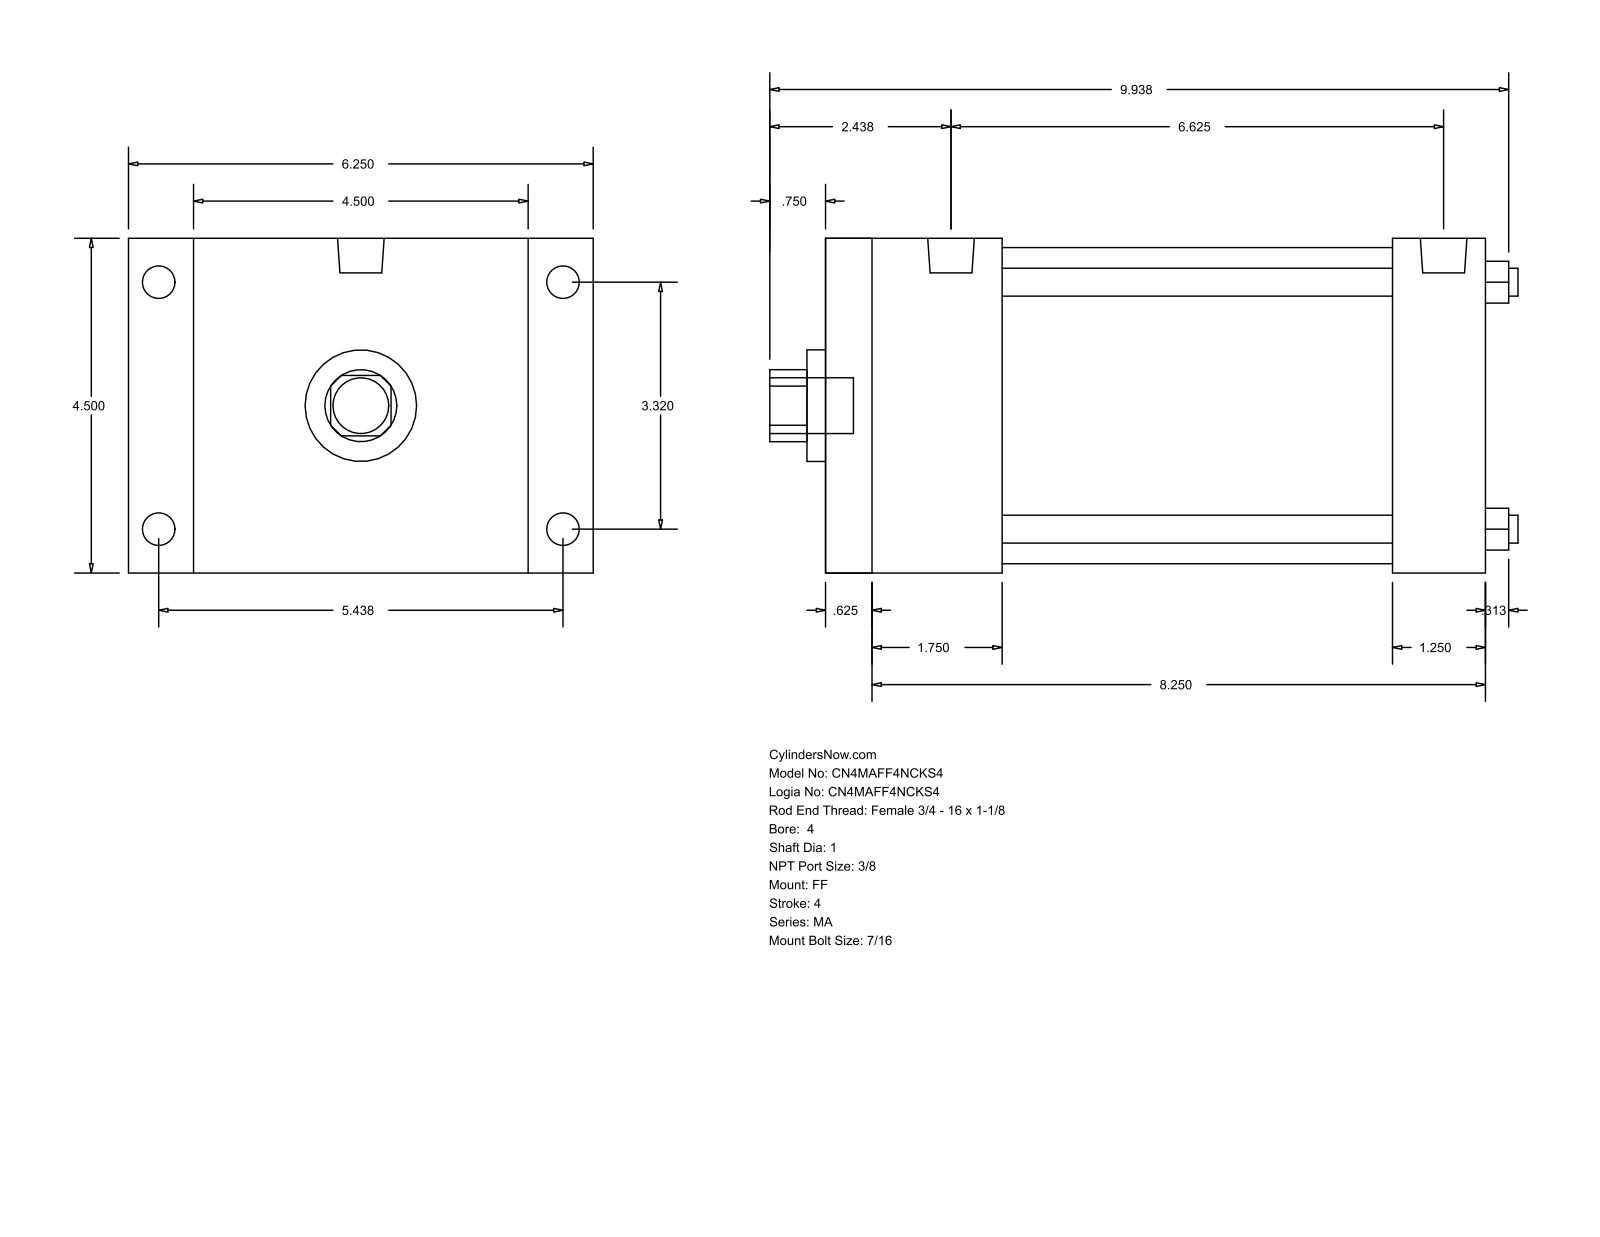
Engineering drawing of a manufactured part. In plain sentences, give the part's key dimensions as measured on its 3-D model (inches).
The part is named "MA_FF__0400_1". Its 3-D file was written by "GSSL Pune (CONFIG_CONTROL_DESIGN)". It is 0 solids with 92 faces: 64 planar, 28 cylindrical and 0 other. Overall it measures 10.063 by 6.25 by 4.5 inches. Round holes: 4 of diameter 0.375, 1 of diameter 1, 1 of diameter 1.5, 1 of diameter 4.25. Round bosses or shafts: 8 of diameter 0.437, 2 of diameter 0.627, 1 of diameter 0.75. Partial cylindrical surfaces (rounded edges, fillets, slot ends): 1 of radius 0.484. The main face-to-face distances are 4.5, 8.875, 0.625, 8.25, 0.875, 5.375, 7.625, 7, 1.25, 2.375. The hole center spacings are 2.347, 3.32, 4.695.
